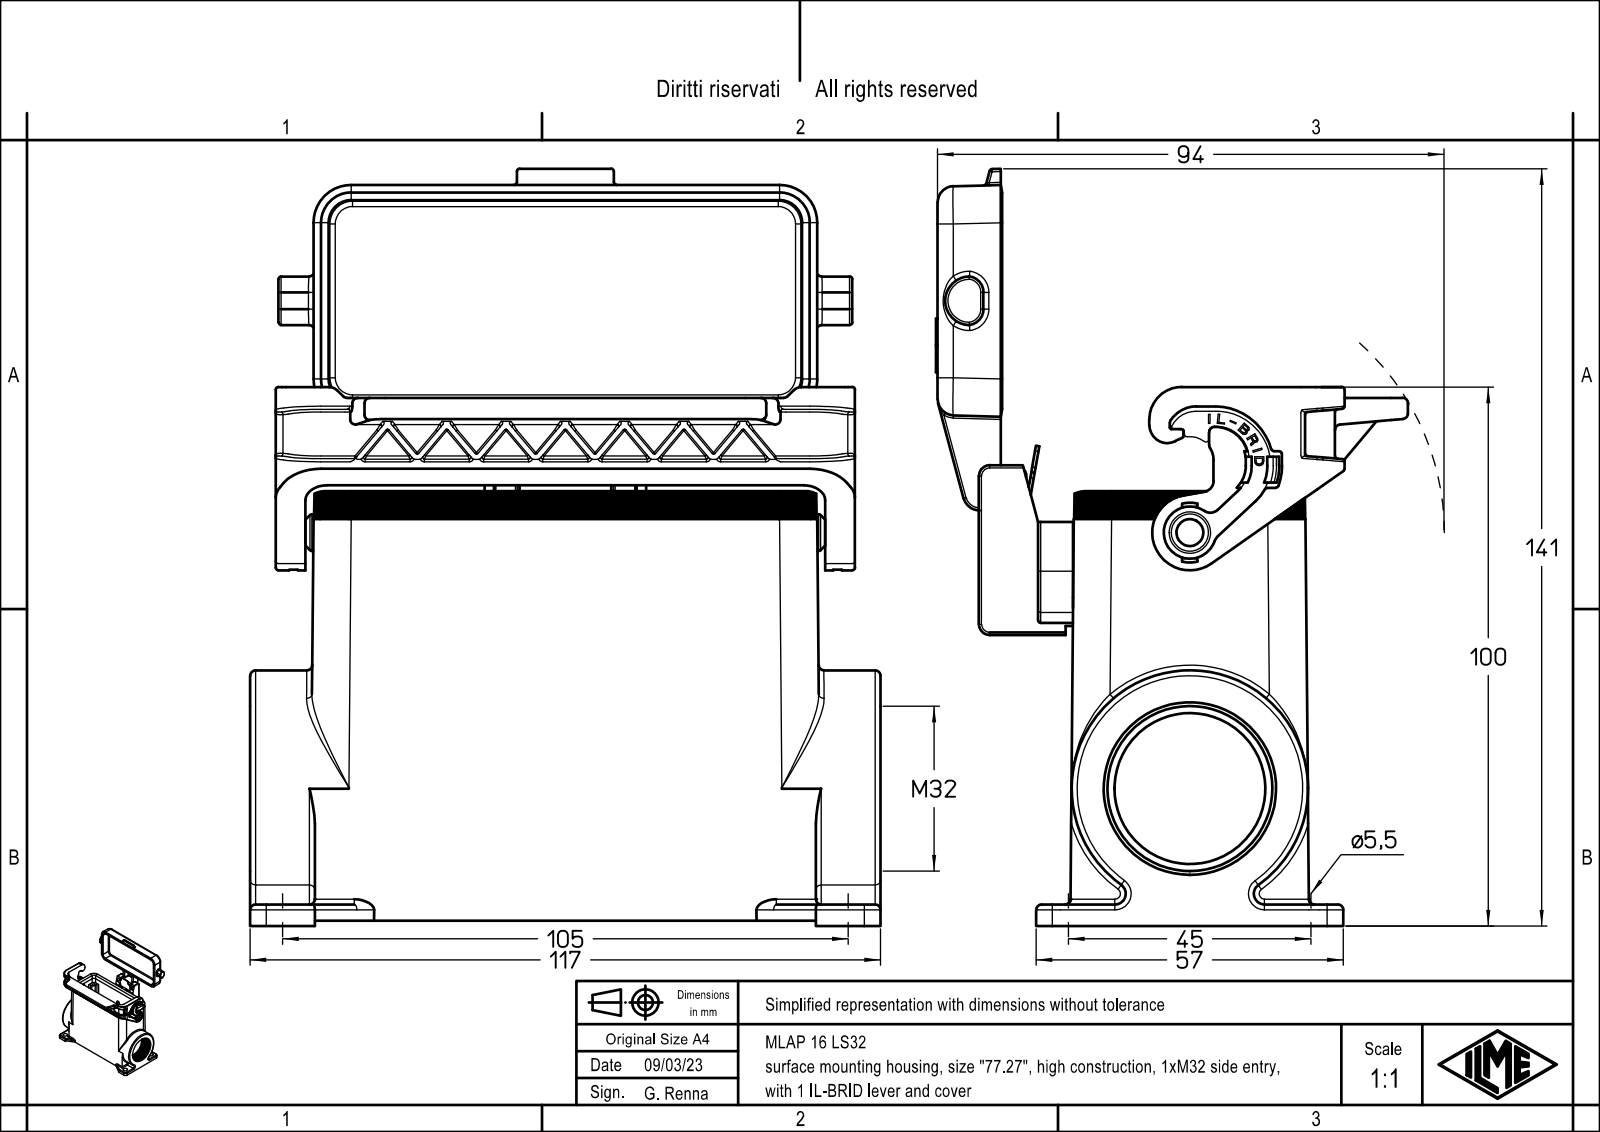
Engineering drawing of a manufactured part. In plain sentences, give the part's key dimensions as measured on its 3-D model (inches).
The part is named "MLAP 16 LS32". Its 3-D file was written by "Creo Elements/Direct Modeling 20.1B 02-Apr-2019 (C) Parametric Technology GmbH (AUTOMOTIVE_DESIGN)". It is 1 solid with 1381 faces: 818 planar, 396 cylindrical and 167 other. Overall it measures 5.531 by 4.606 by 3.457 inches. Its volume is 10.76 cubic inches and its surface area 137 square inches. Round holes: 4 of diameter 0.118, 4 of diameter 0.138, 3 of diameter 0.217, 1 of diameter 0.128, 1 of diameter 0.213, 1 of diameter 0.303, 1 of diameter 1.102, 1 of diameter 1.205. Round bosses or shafts: 1 of diameter 1.727, 1 of diameter 0.331, 1 of diameter 0.272, 1 of diameter 0.268, 1 of diameter 0.205, 1 of diameter 0.126. Partial cylindrical surfaces (rounded edges, fillets, slot ends): 28 of radius 0.02, 27 of radius 0.004, 23 of radius 0.008, 23 of radius 0.039, 23 of radius 0.118, 17 of radius 0.007, 16 of radius 0.013, 15 of radius 0.079. The main face-to-face distances are 0.079, 0.118, 0.11, 2.746, 2.825, 0.404, 4.203, 0.039, 0.276, 0.157. The hole center spacings are 0.647, 1.517, 3.61, 3.862, 1.063, 3.051, 3.231, 1.772.
